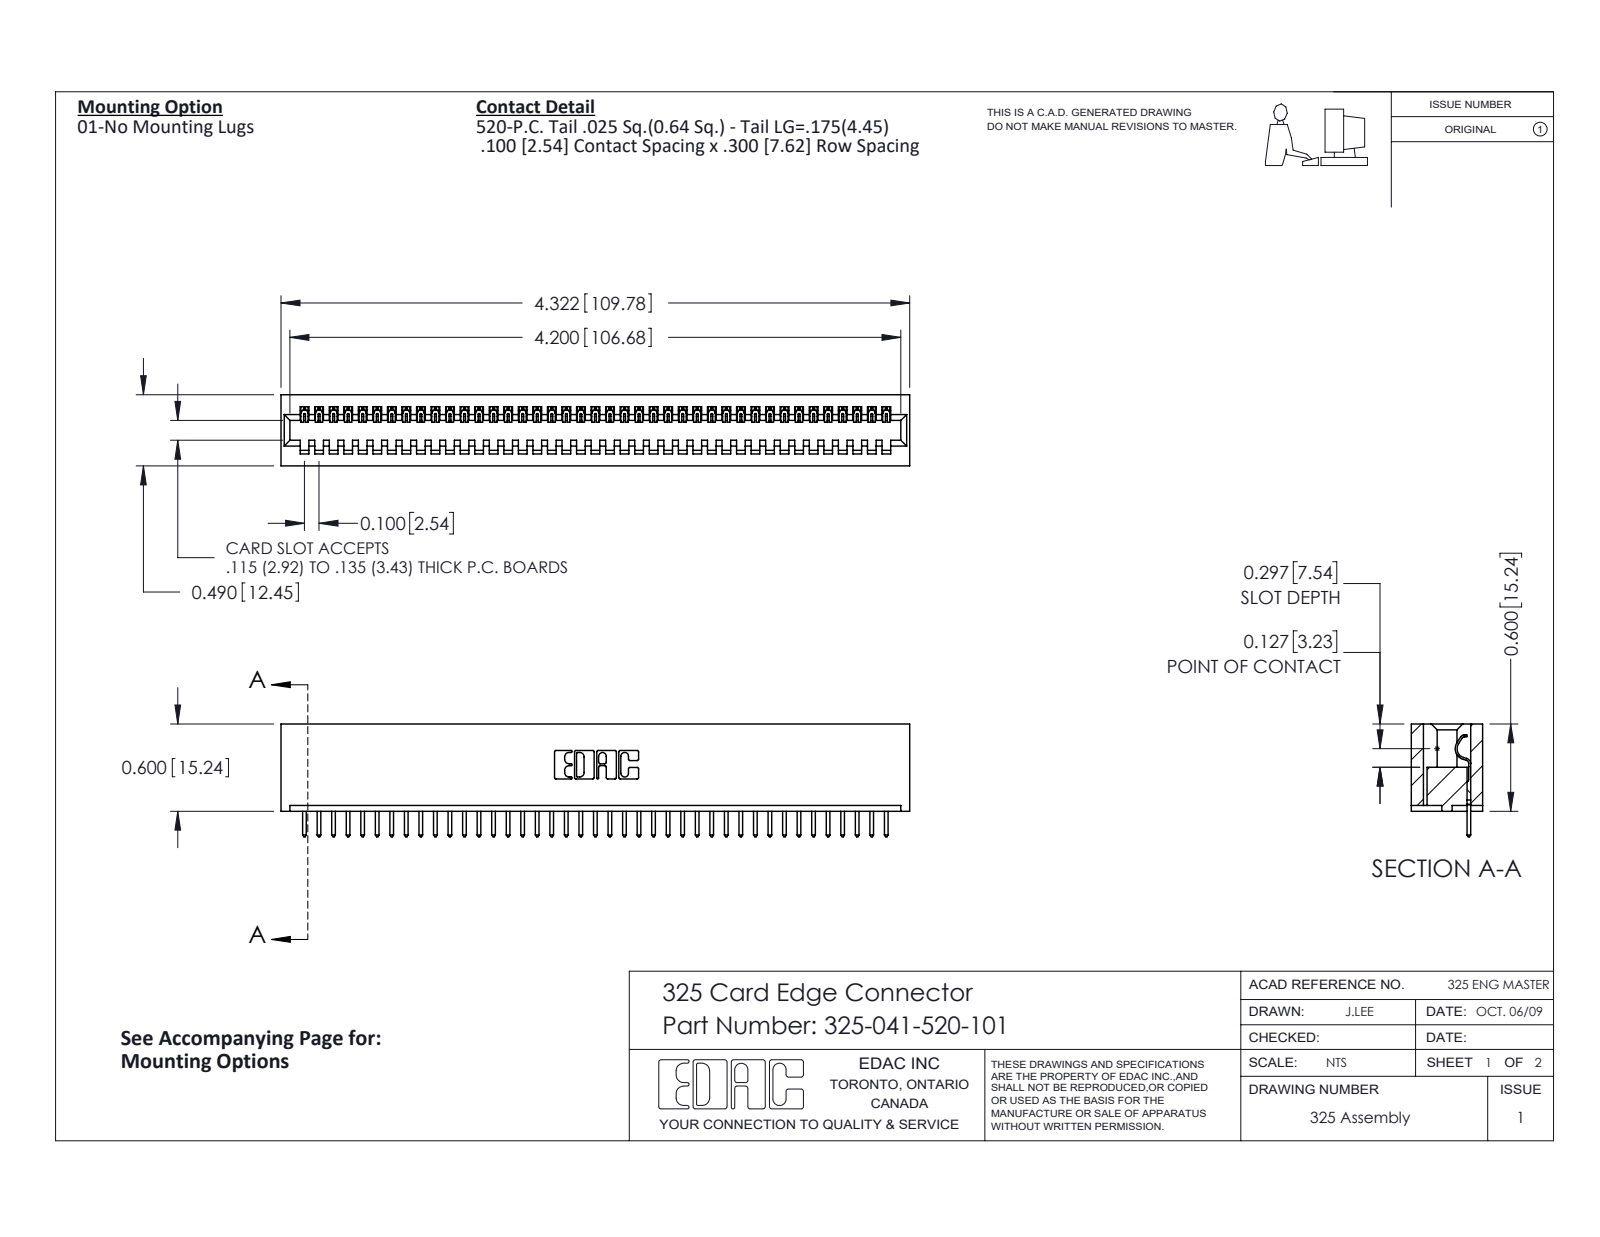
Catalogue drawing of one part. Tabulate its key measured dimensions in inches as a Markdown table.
| quantity | value |
| --- | --- |
| part name | 325 Part_Lugless; 325-041-520-101; 325-292-001_325-293-120 |
| STEP written by | SolidWorks 2016 (CONFIG_CONTROL_DESIGN) |
| units | inches |
| bodies | 42 solids, 2484 faces (1788 planar, 696 cylindrical, 0 other) |
| overall size | 4.322 × 0.775 × 0.49 |
| volume | 0.878 in³ |
| surface area | 24.44 in² |
| partial cylindrical surfaces (radius × count) | 0.006 × 82, 0.01 × 82, 0.01 × 22, 0.007 × 6, 0.031 × 6, 0.026 × 3, 0.014 × 1, 0.022 × 1 |
| main face-to-face distances | 0.083, 0.407, 0.49, 0.3, 0.107, 0.383, 0.025, 0.325, 0.56, 0.263 |
